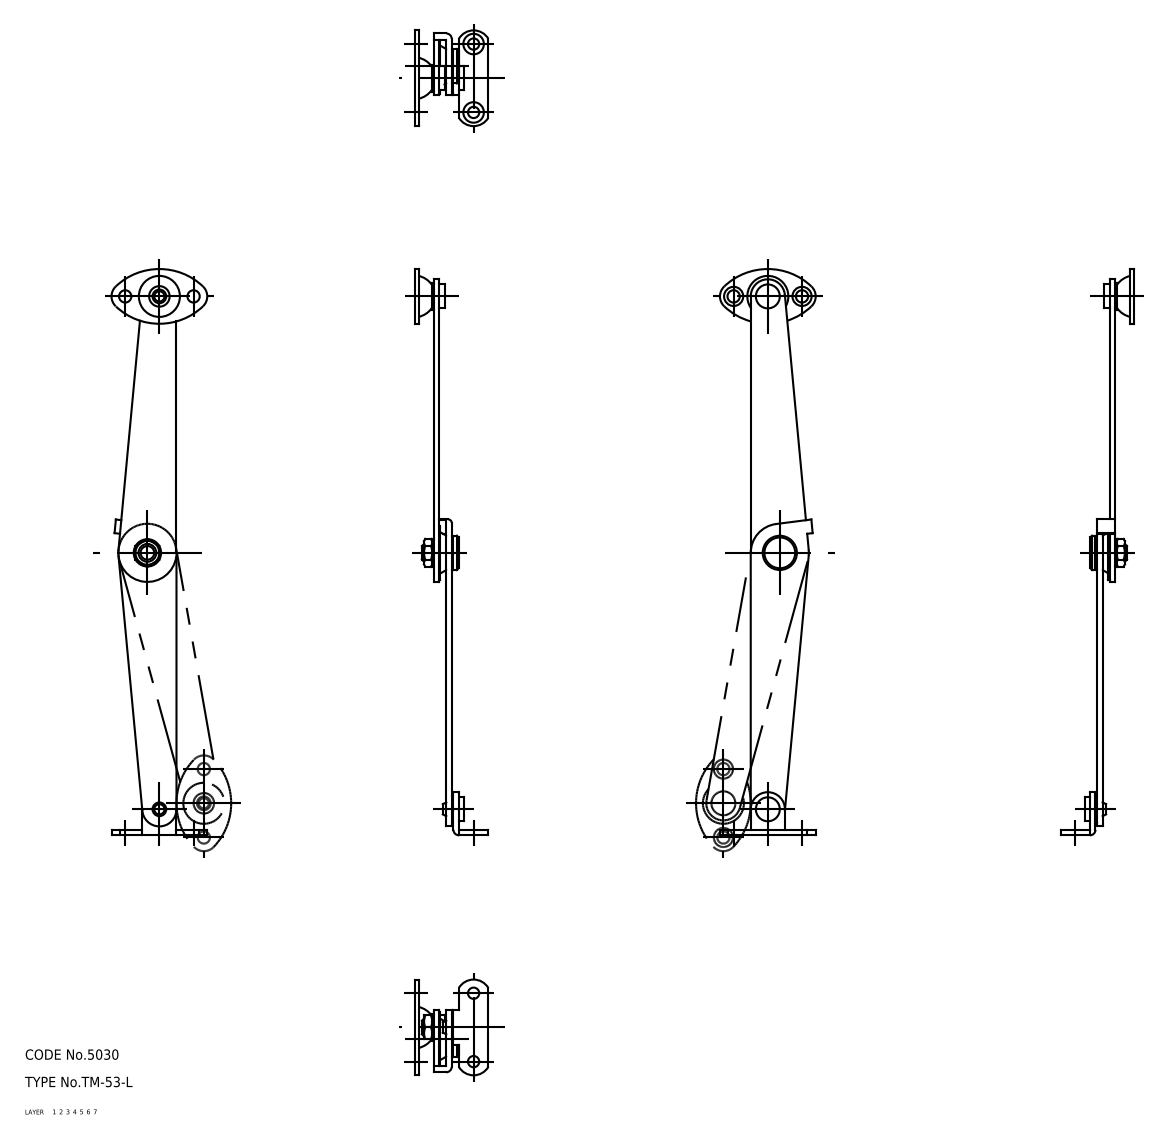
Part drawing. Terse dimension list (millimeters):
name: rivet_A; rivet_B; washer_2; washer_3 (+7 more)
written by: CADfix (AUTOMOTIVE_DESIGN)
unit: mm
bodies: 12 solids, 142 faces (0 planar, 0 cylindrical, 142 other)
size: 165.6 × 28 × 21.4
volume: 5 333 mm³; area: 8 537 mm²
